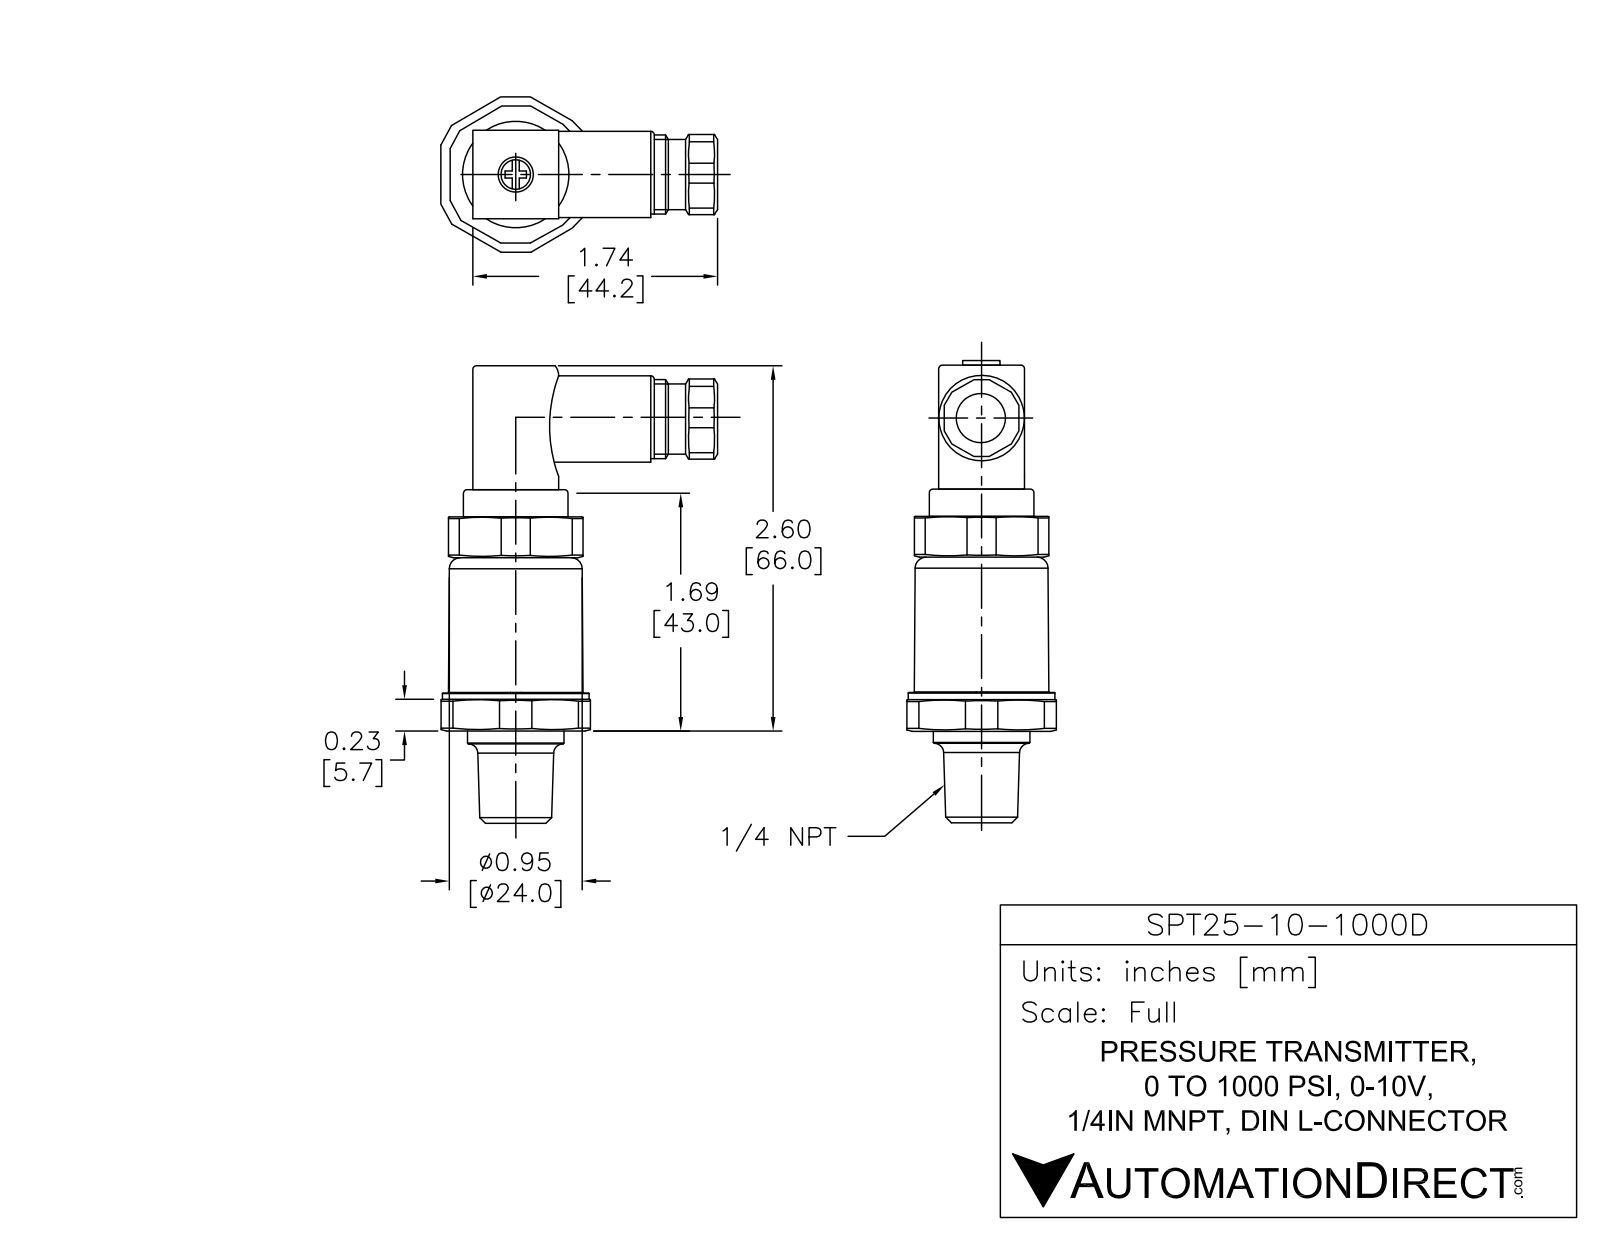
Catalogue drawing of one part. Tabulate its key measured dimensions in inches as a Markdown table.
| quantity | value |
| --- | --- |
| part name | SPT25-10-1000D |
| STEP written by | SolidWorks 2013 (AUTOMOTIVE_DESIGN) |
| units | inches |
| bodies | 5 solids, 200 faces (96 planar, 87 cylindrical, 17 other) |
| overall size | 3.199 × 1.496 × 1.406 |
| volume | 1.702 in³ |
| surface area | 15.71 in² |
| round holes (diameter × count) | 0.039 × 1, 0.13 × 1, 0.276 × 1, 0.315 × 1 |
| round bosses / shafts (diameter × count) | 1.053 × 1, 0.945 × 1, 0.689 × 1, 0.591 × 1, 0.551 × 1, 0.433 × 1 |
| partial cylindrical surfaces (radius × count) | 0.059 × 8, 0.045 × 4, 0.089 × 4, 0.079 × 3, 0.045 × 1, 0.046 × 1, 0.571 × 1 |
| main face-to-face distances | 0.059, 1.161, 1.22, 0.62, 0.014, 0.606, 0.266, 1.486, 1.427, 0.197 |
| hole center spacings | 0.052 |
